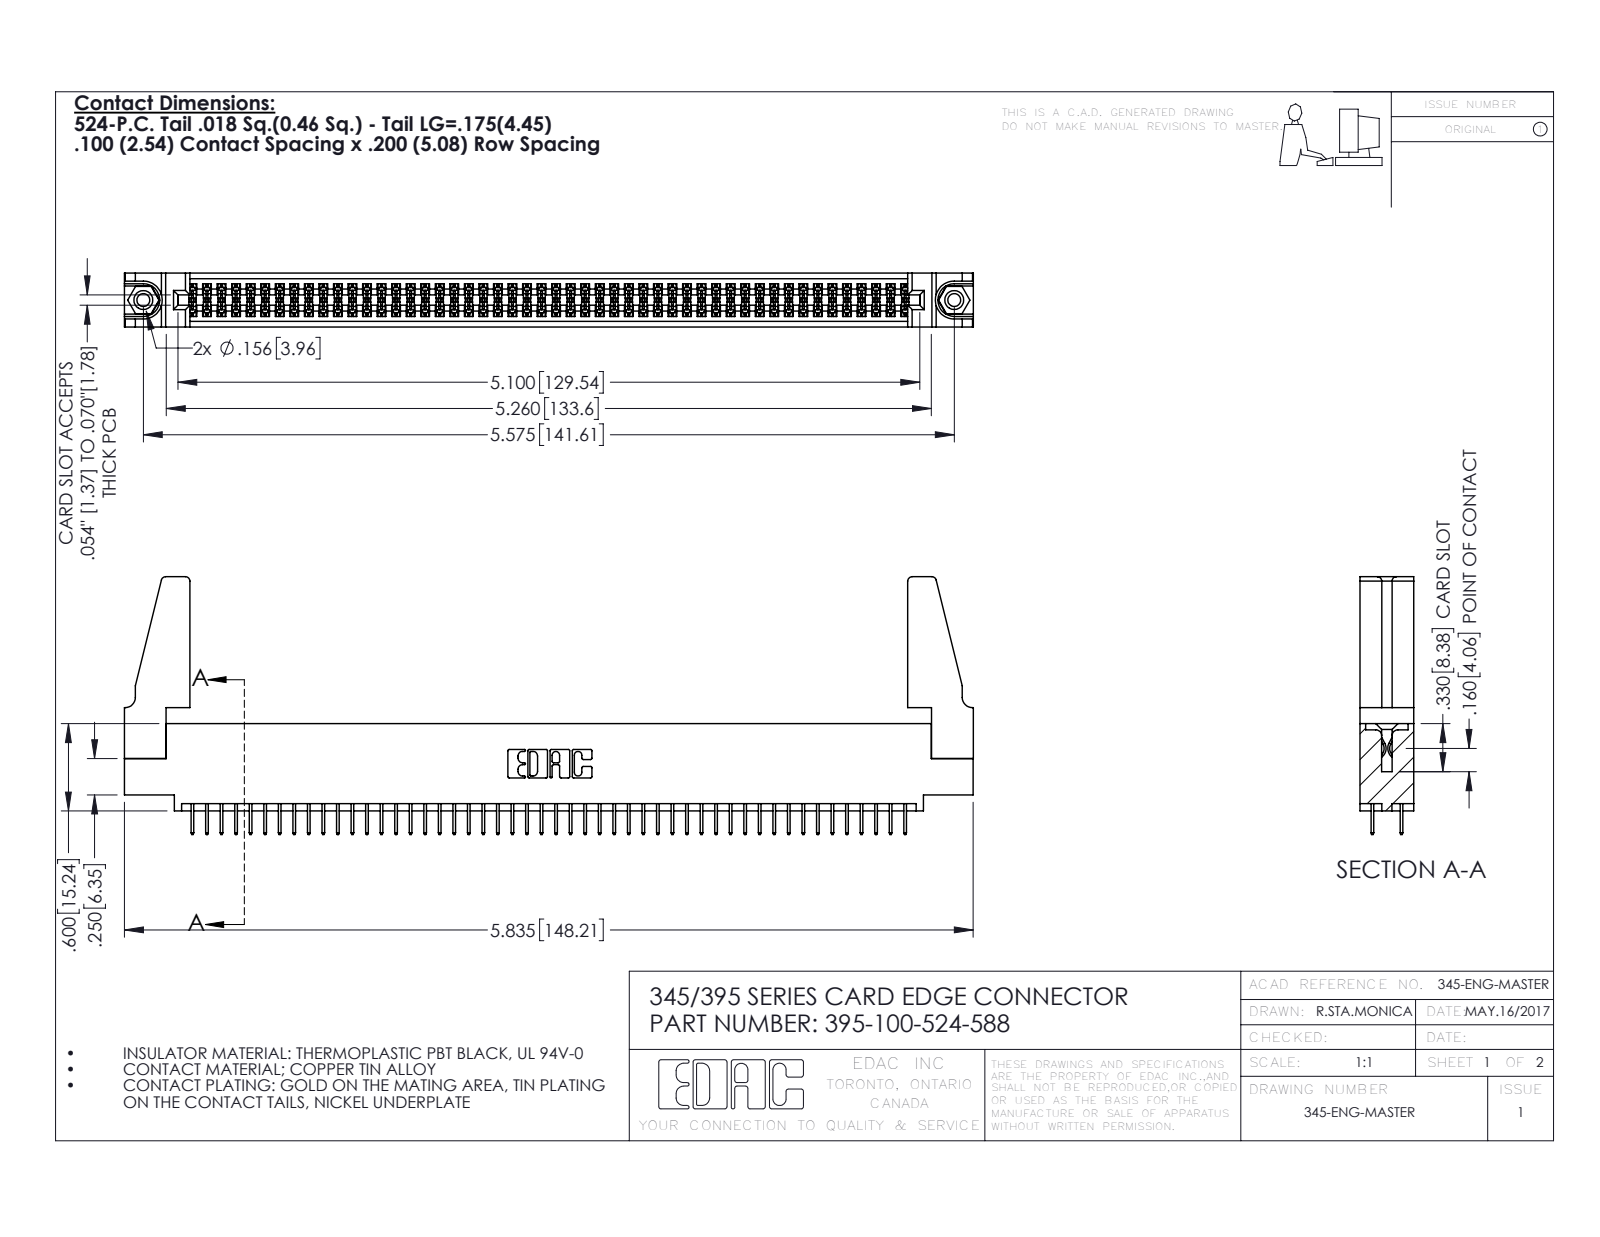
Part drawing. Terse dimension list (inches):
name: 345-220-078_345-220-088; 345-250-001_345-250-001-102; 345 Part_0.110 Offset - 0.156 Dia-TH; 345-292-001_345-293-124 (+1 more)
written by: SolidWorks 2016 (CONFIG_CONTROL_DESIGN)
unit: in
bodies: 105 solids, 5654 faces (4056 planar, 1582 cylindrical, 16 other)
size: 5.836 × 1.772 × 0.37
volume: 1.068 in³; area: 37.25 in²
holes: 2× ⌀0.089, 2× ⌀0.125, 2× ⌀0.156, 1× ⌀0.064
bosses: 2× ⌀0.155
rounds: 150× R0.006, 22× R0.01, 8× R0.03, 6× R0.007, 6× R0.031, 3× R0.026, 2× R0.014, 2× R0.019
face distances: 0.072, 0.298, 0.37, 0.2, 0.098, 0.272, 0.025, 0.225, 0.072, 0.175
hole spacings: 0.27, 5.339, 5.575
